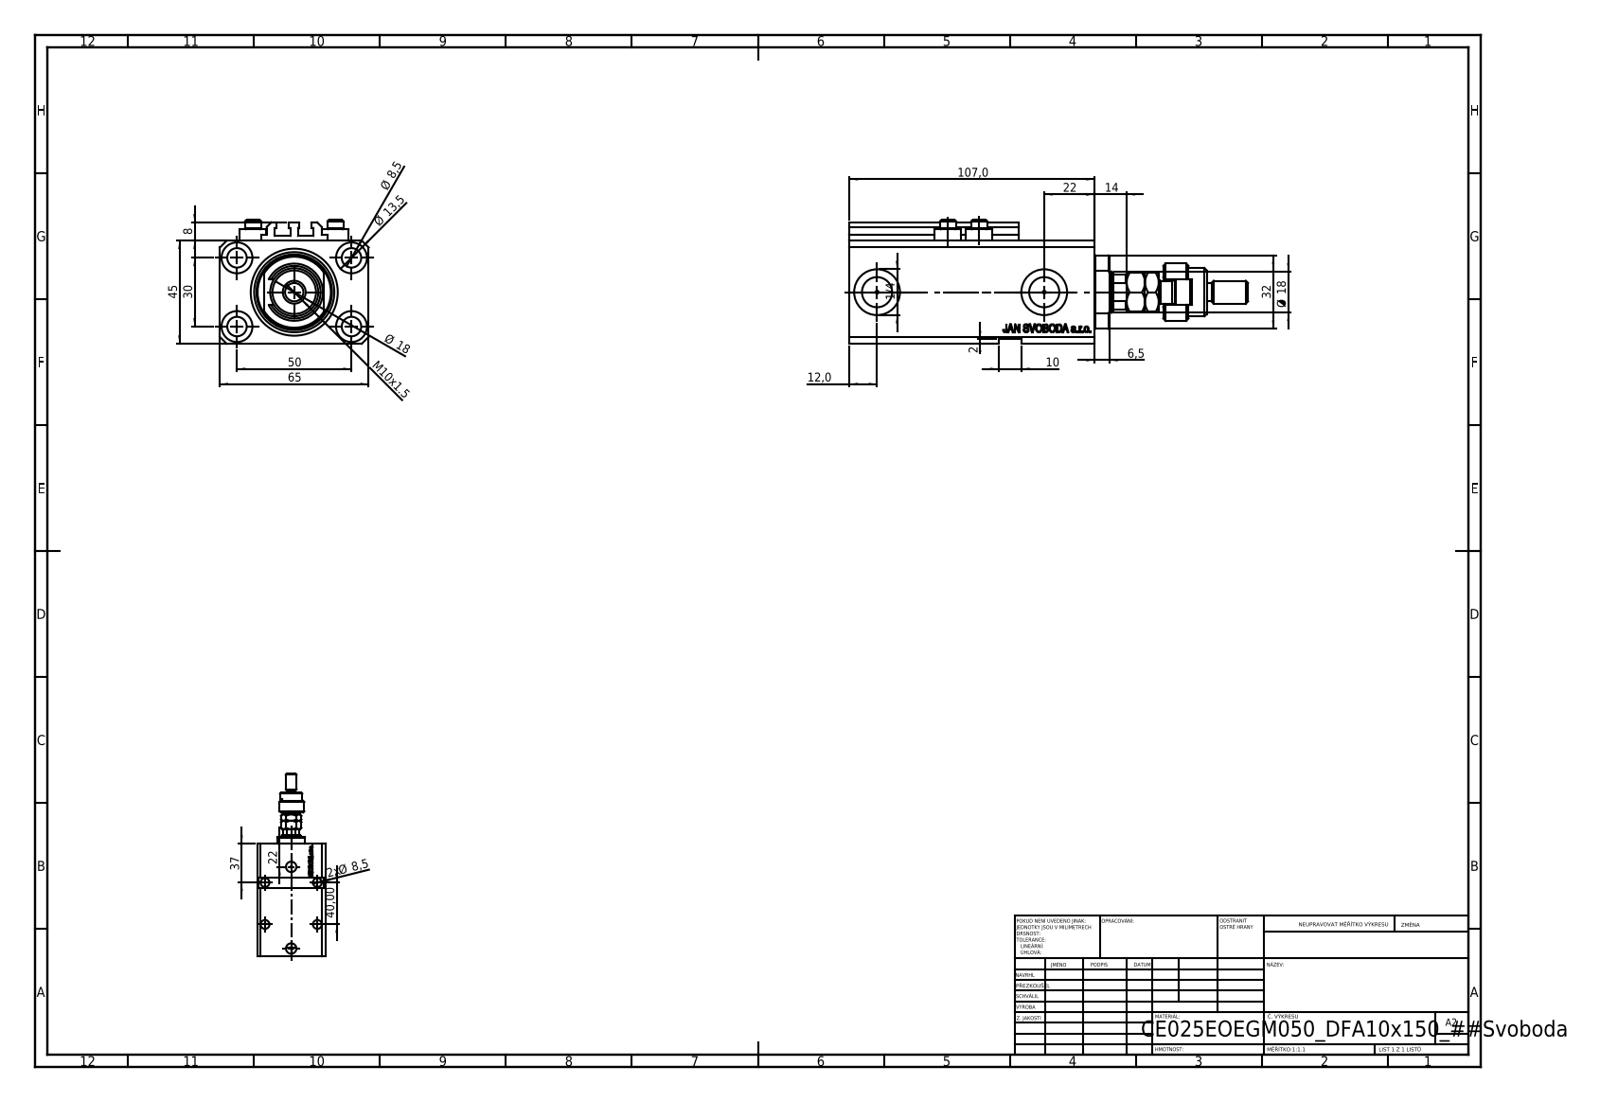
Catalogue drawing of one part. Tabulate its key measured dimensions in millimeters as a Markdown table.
| quantity | value |
| --- | --- |
| part name | ALLEN BOLT V250CE; V250CE_VC_E; MFA; FEMALE_PART_FOR_DFA (+2 more) |
| STEP written by | SolidWorks 2019 (CONFIG_CONTROL_DESIGN) |
| units | millimeters |
| bodies | 10 solids, 1172 faces (539 planar, 159 cylindrical, 474 other) |
| overall size | 174 × 65 × 54 |
| volume | 285 194 mm³ |
| surface area | 82 321 mm² |
| round holes (diameter × count) | 8.5 × 9, 1.25 × 4, 4 × 4, 13.5 × 4, 10 × 2, 13.16 × 2, 20 × 2, 18 × 1, 38 × 1 |
| round bosses / shafts (diameter × count) | 11.6 × 4, 7 × 4, 25 × 1, 21 × 1, 16 × 1, 10 × 1, 8 × 1 |
| partial cylindrical surfaces (radius × count) | 0.2 × 10, 5.5 × 1, 8.5 × 1, 8.75 × 1, 16 × 1 |
| main face-to-face distances | 45, 65, 14, 2, 93, 47, 107, 2.5, 3, 10 |
| hole center spacings | 29.15, 50, 13.6, 14.76, 15.12, 27.51, 27.89, 30 |
